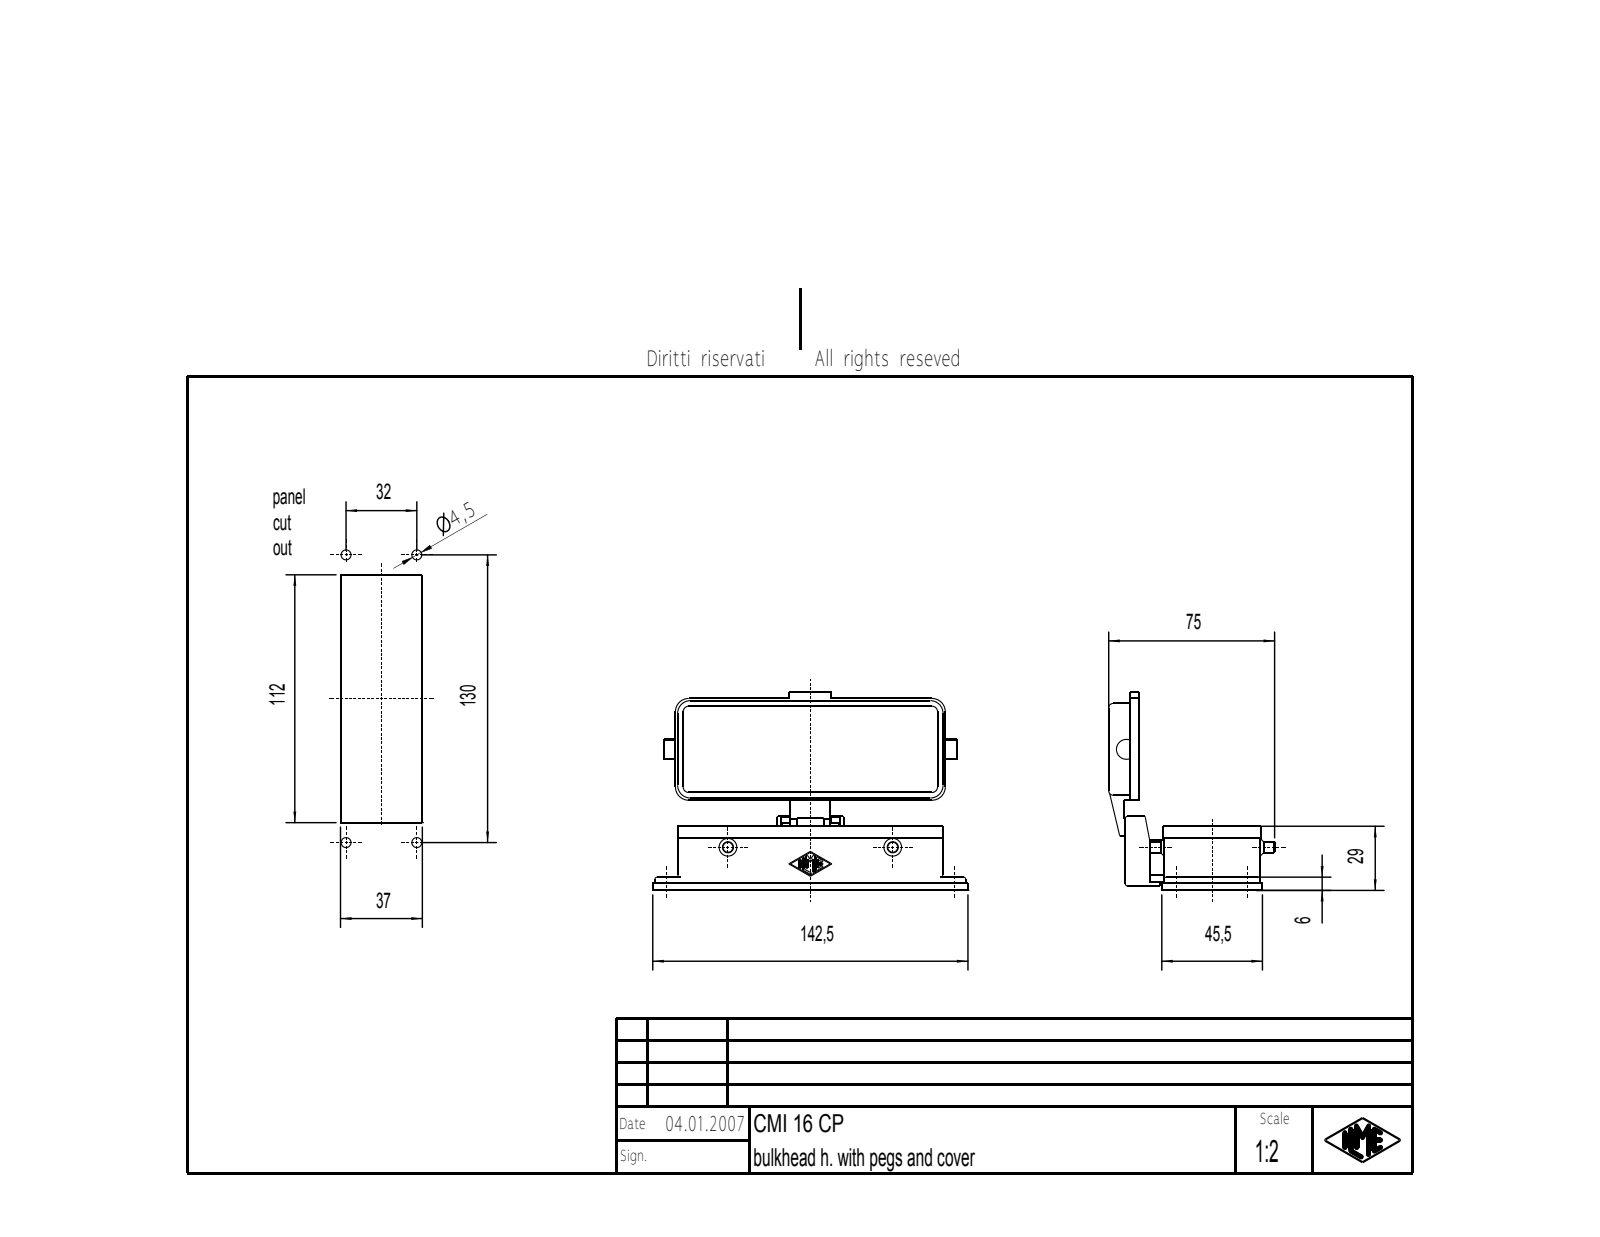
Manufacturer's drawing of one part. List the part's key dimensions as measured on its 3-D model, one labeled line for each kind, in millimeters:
Part name (STEP PRODUCT): CMI 16 CP
STEP written by: Autodesk Inventor 7 (AUTOMOTIVE_DESIGN)
Units: millimetres
Bodies: 1 solid, 470 faces (205 planar, 179 cylindrical, 86 other)
Overall size (bounding box): 142.5 × 89.75 × 75
Volume: 65 629 mm³ · Surface area: 49 694 mm²
Round holes (diameter × count): ⌀4.5 ×4, ⌀4.6 ×4, ⌀4 ×1, ⌀5 ×1
Round bosses / shafts (diameter × count): ⌀5 ×2, ⌀3 ×2, ⌀7 ×1, ⌀4 ×1
Partial cylindrical surfaces — rounded edges, fillets, slot ends (radius × count): R0.38 ×14, R6 ×12, R0.5 ×10, R0.7 ×8, R1 ×8, R2 ×8, R2.5 ×8, R3 ×4
Main face-to-face distances: 2.5, 3, 40.5, 4, 40.75, 1.25, 0.75, 1, 25.5, 43.75
Hole centre spacings: 32, 130, 133.88
